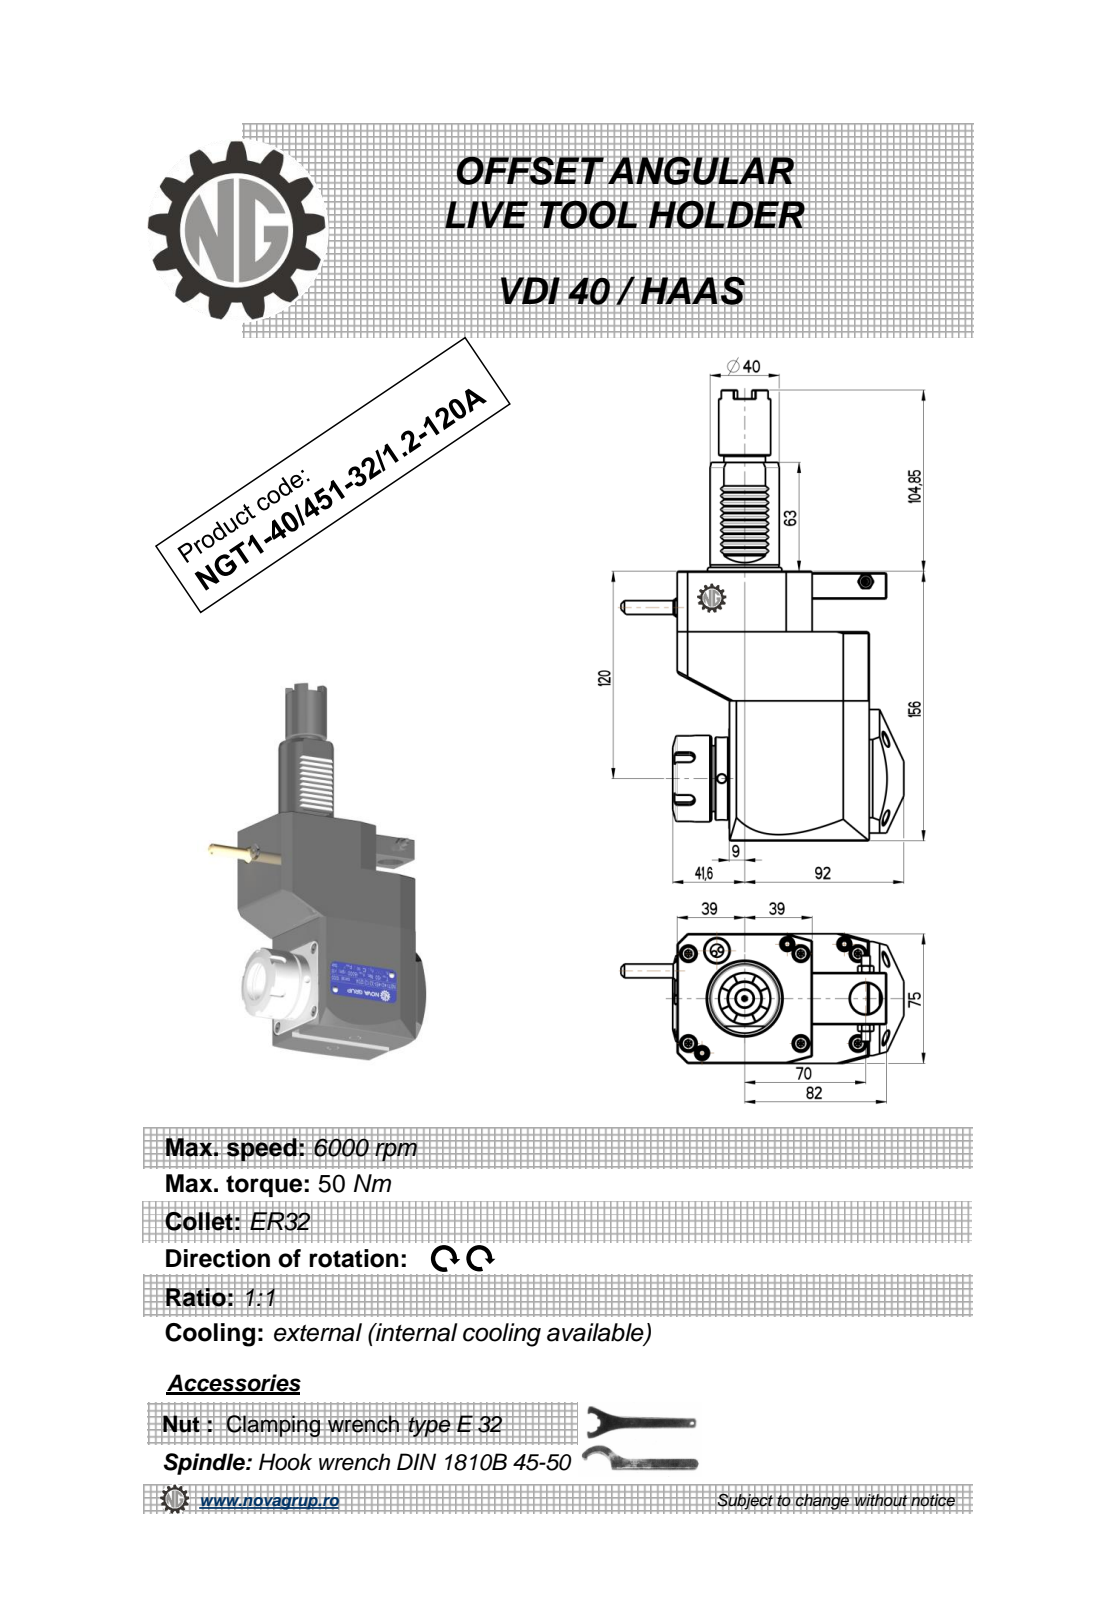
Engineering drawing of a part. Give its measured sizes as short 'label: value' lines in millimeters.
name: NGT1_40_451_32_1_2_120A
written by: PRO/ENGINEER BY PARAMETRIC TECHNOLOGY CORPORATION, 2010280 (CONFIG_CONTROL_DESIGN)
unit: mm
bodies: 1 solid, 464 faces (230 planar, 97 cylindrical, 137 other)
size: 260.85 × 163.5 × 76.6
volume: 1 222 000 mm³; area: 93 520 mm²
holes: 3× ⌀5, 1× ⌀3, 1× ⌀4.2, 1× ⌀9.5, 1× ⌀18, 1× ⌀26.8, 1× ⌀27
bosses: 1× ⌀50, 1× ⌀48, 1× ⌀41, 1× ⌀40, 1× ⌀30, 1× ⌀26.58, 1× ⌀24, 1× ⌀10
rounds: 12× R0.26, 10× R0.3, 6× R0.2, 5× R3, 1× R0.5, 1× R9.75, 1× R40
face distances: 75, 156, 111, 30, 121, 35, 81, 33, 48, 78
hole spacings: 13.25, 20.93, 70, 83.25, 100.28, 112.5, 141.16
